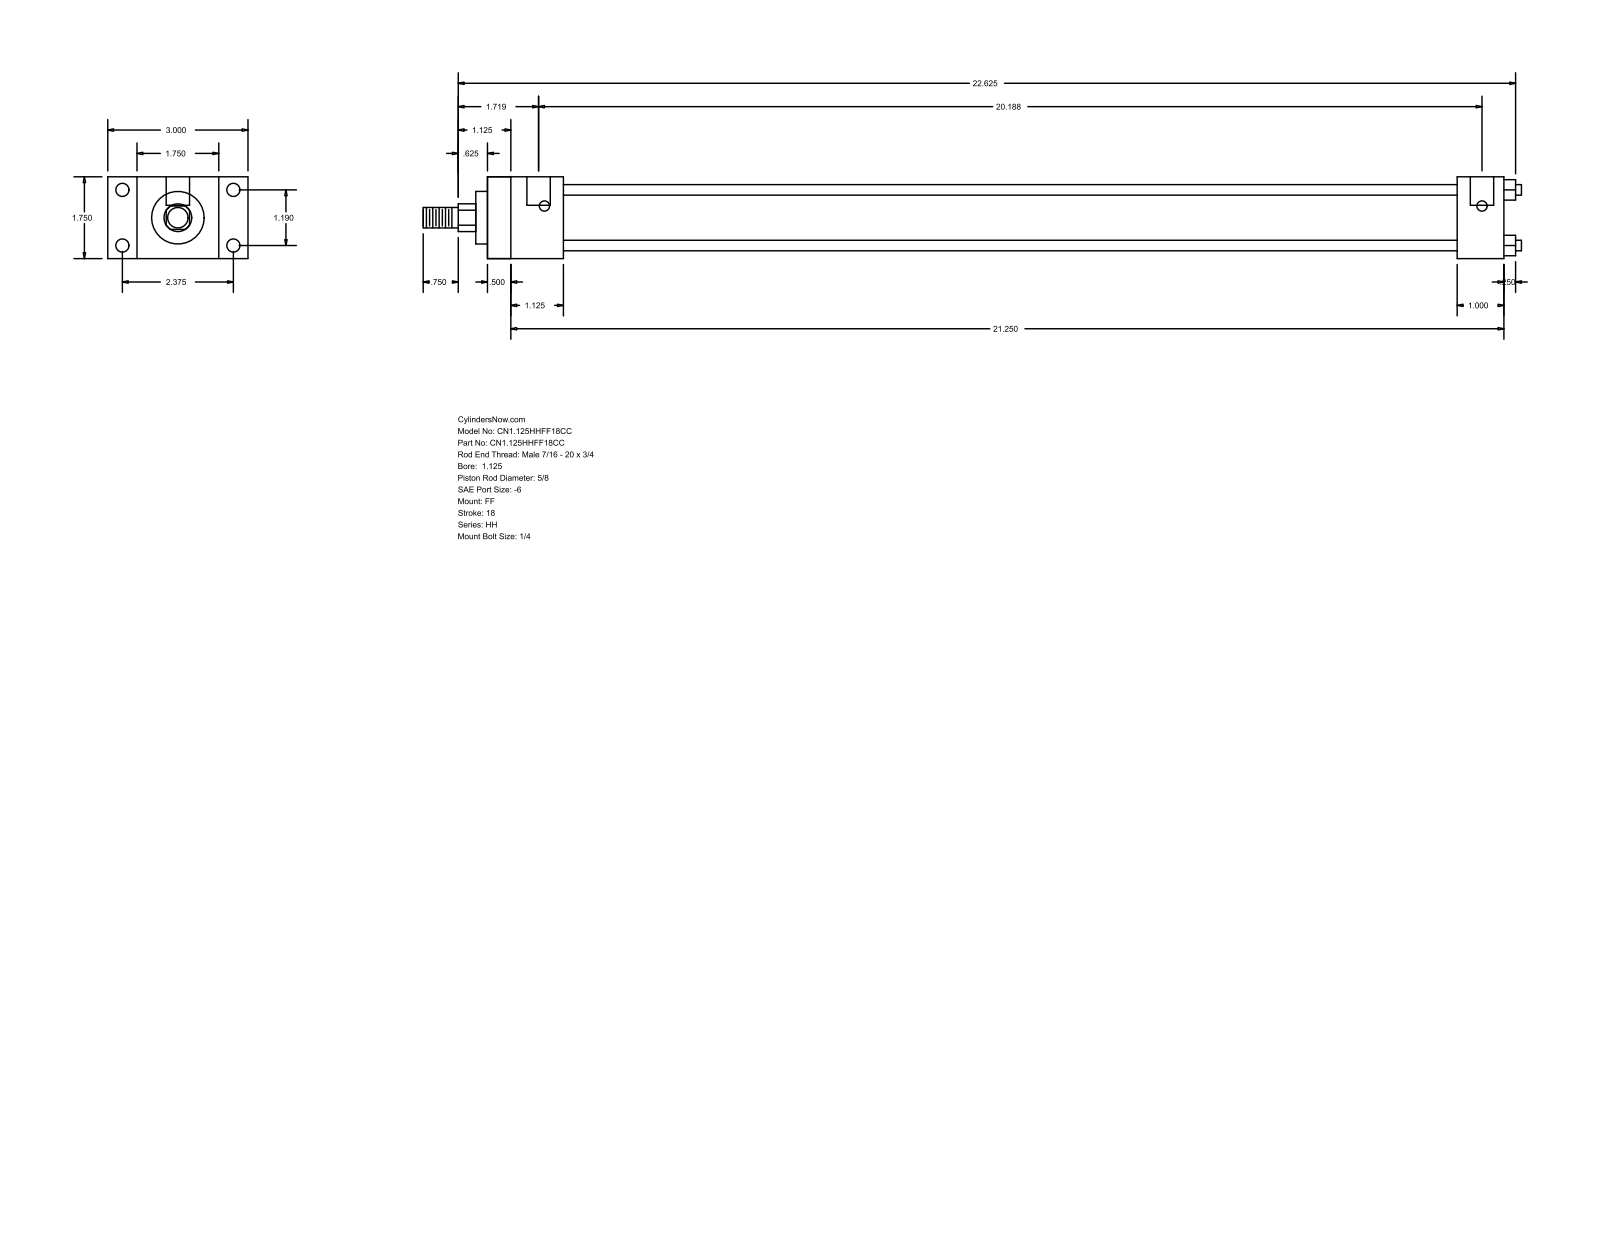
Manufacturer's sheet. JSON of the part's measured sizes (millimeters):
{"part_name": "HH_FF__0112_0.625", "step_written_by": "GSSL Pune (CONFIG_CONTROL_DESIGN)", "units": "millimeters", "bodies": {"solids": 0, "faces": 92, "planar": 64, "cylindrical": 28, "other": 0}, "overall_size": [596.9, 76.2, 44.45], "round_holes": [[5.56, 4], [7.14, 4], [12.7, 2]], "round_bosses_or_shafts": [[5.71, 4], [34.92, 1], [28.57, 1], [15.88, 1], [11.11, 1]], "partial_cylinders_radius": [[7.54, 1]], "face_to_face_distances": [44.46, 552.45, 12.69, 539.76, 15.87, 28.58, 60.33, 41.27, 527.04, 514.35], "hole_center_spacings": [30.22, 60.32, 67.47, 509.59, 3.17, 512.76]}
